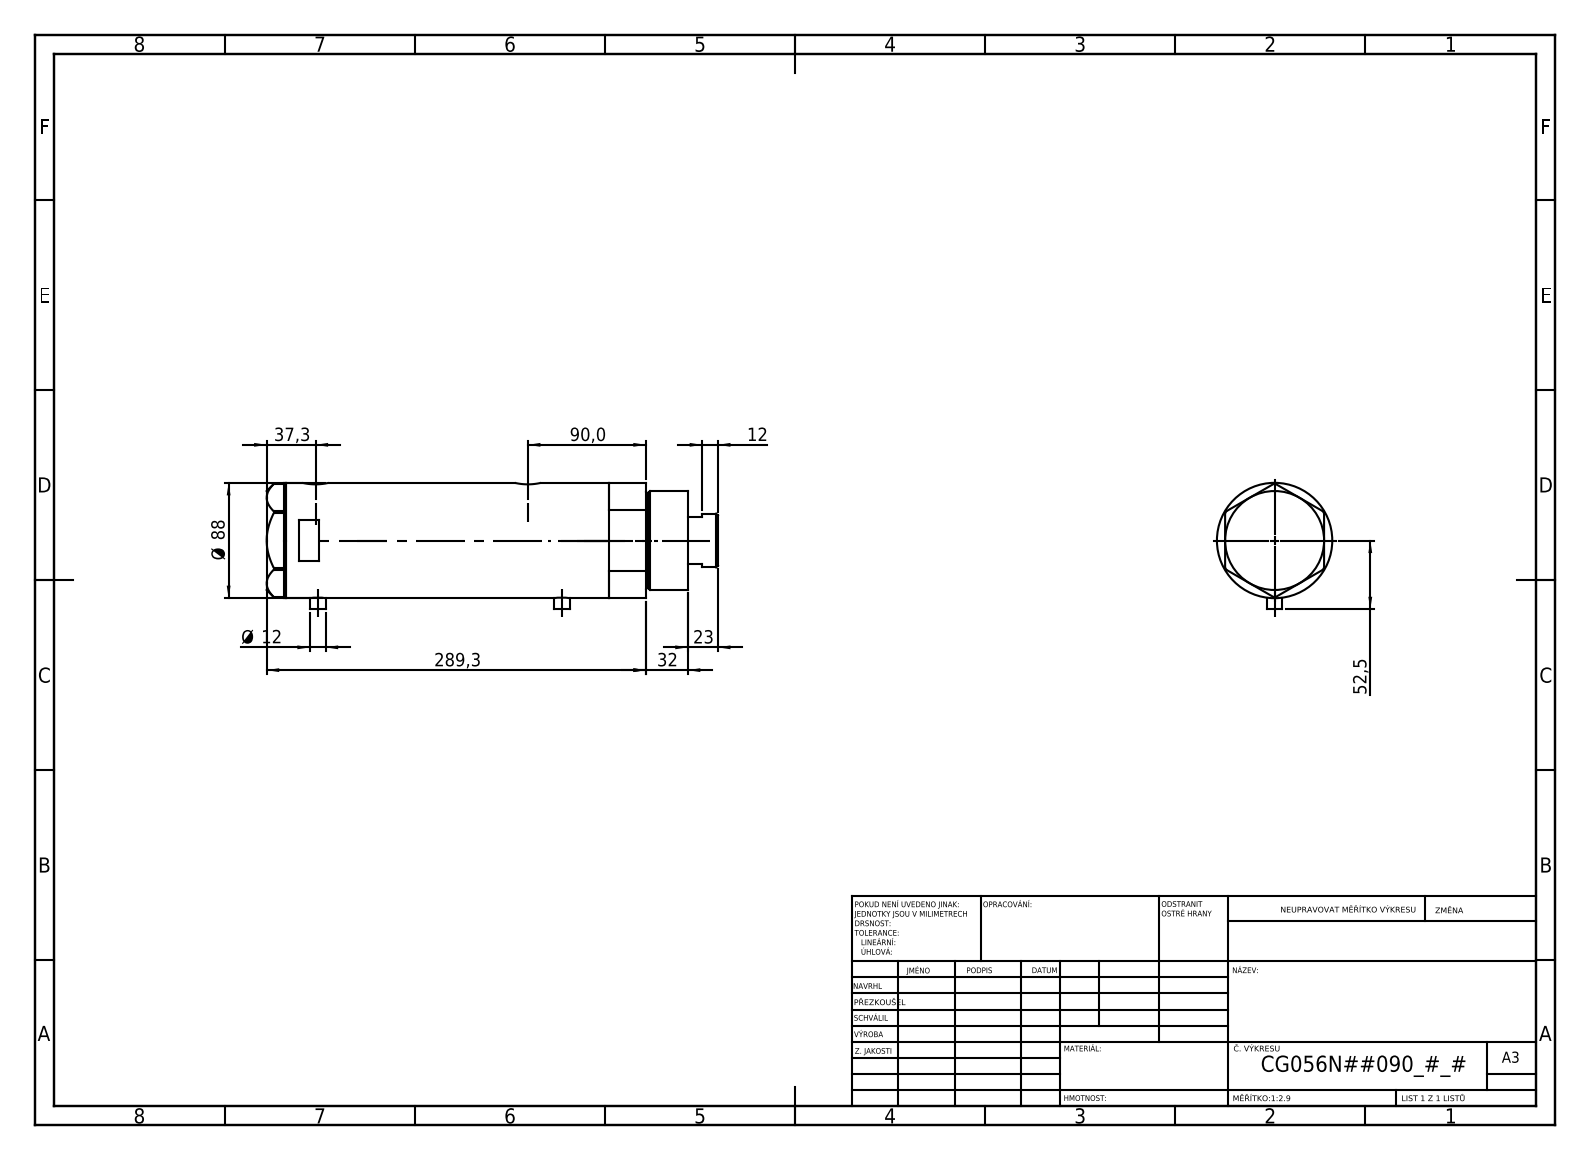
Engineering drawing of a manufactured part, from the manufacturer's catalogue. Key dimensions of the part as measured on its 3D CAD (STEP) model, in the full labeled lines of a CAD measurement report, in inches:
Part name (STEP PRODUCT): V270CG_VC; V270CG_FRONT; V270CG_MIDDLE; V270CG_BACK
STEP written by: SolidWorks 2019 (CONFIG_CONTROL_DESIGN)
Units: inches
Bodies: 4 solids, 121 faces (52 planar, 49 cylindrical, 20 other)
Overall size (bounding box): 13.555 × 3.799 × 3.465
Volume: 109.5 in³ · Surface area: 389.2 in²
Round holes (diameter × count): ⌀0.492 ×2, ⌀0.518 ×2, ⌀0.787 ×2, ⌀0.571 ×1, ⌀1.654 ×1, ⌀1.713 ×1, ⌀2.205 ×1, ⌀2.362 ×1, ⌀3.15 ×1
Round bosses / shafts (diameter × count): ⌀0.472 ×2, ⌀3.465 ×1, ⌀2.953 ×1, ⌀2.874 ×1, ⌀1.614 ×1
Main face-to-face distances: 7.26, 1.024, 6.236, 0.591, 1.614, 7.85, 12.059, 12.65, 11.035, 4.799
Hole centre spacings: 0.067, 1.016, 6.311, 6.378, 7.327, 7.394
